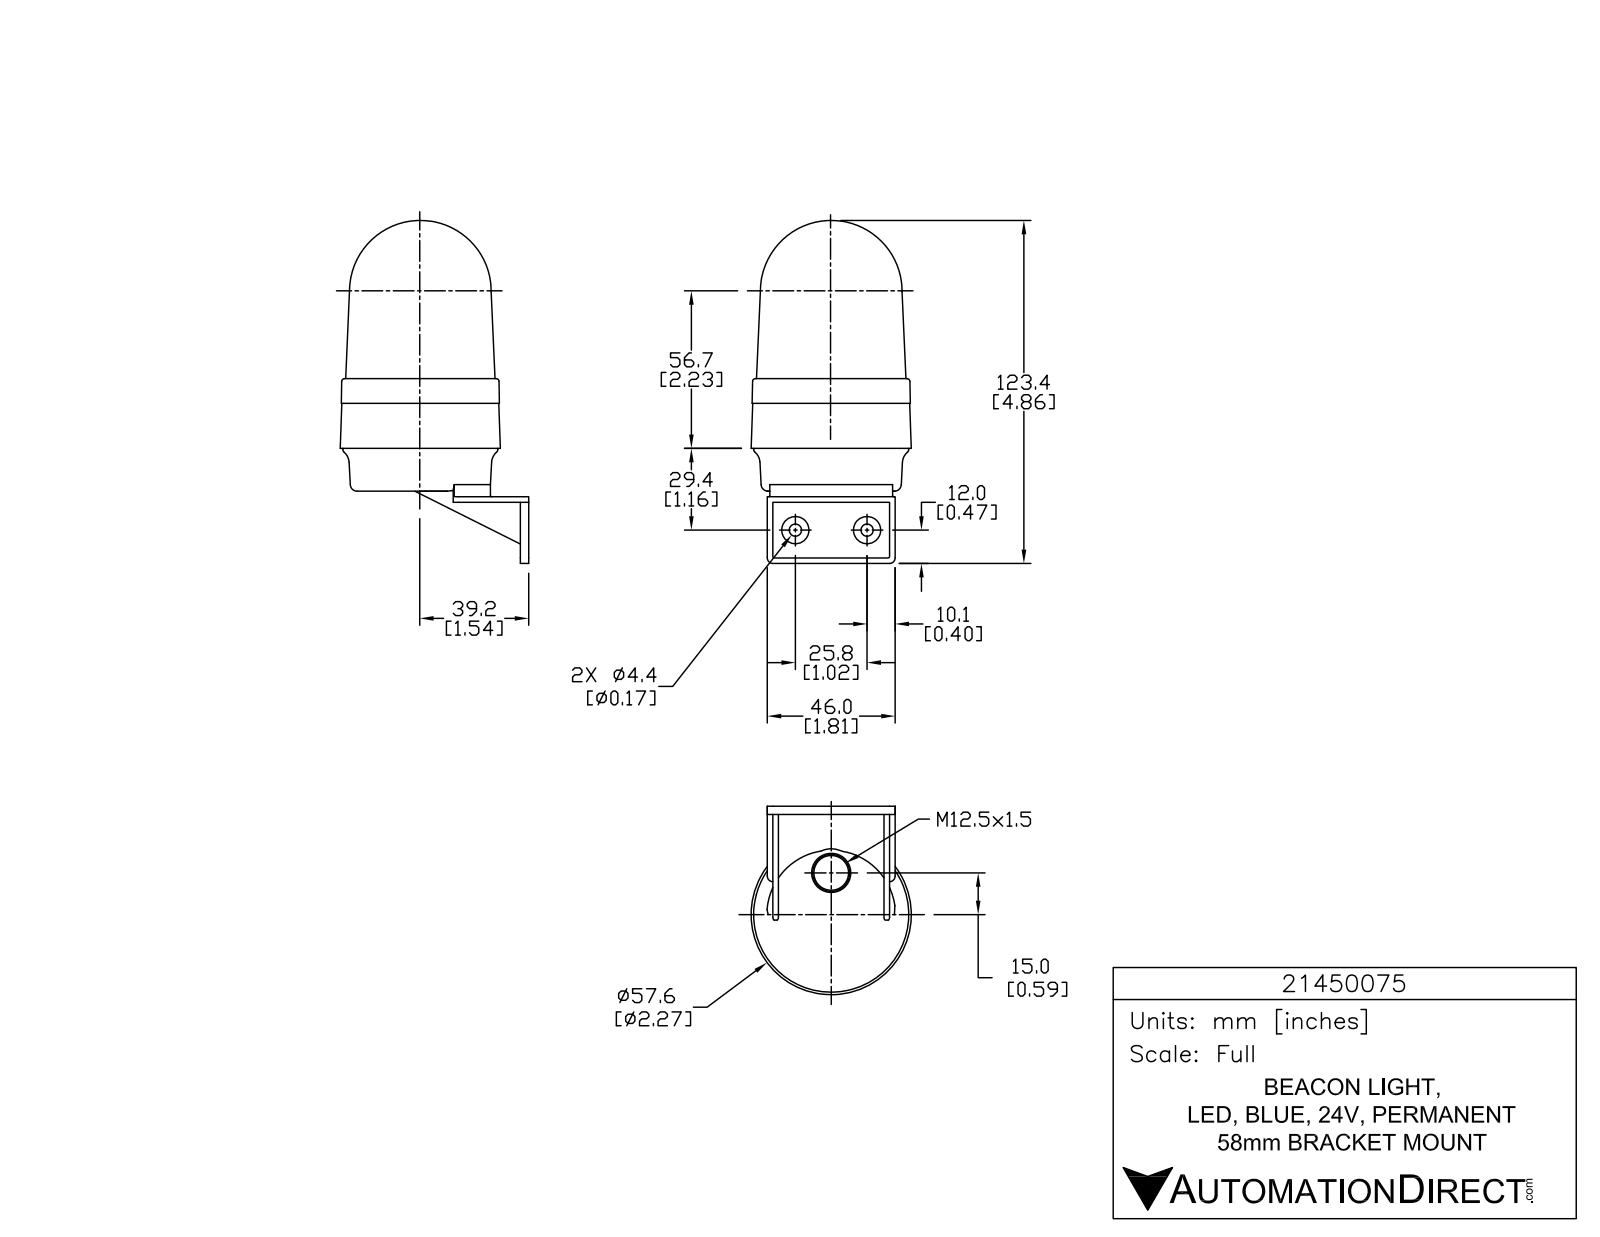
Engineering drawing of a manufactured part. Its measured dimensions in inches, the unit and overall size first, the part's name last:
Units: inches
Overall size (bounding box): 4.858 × 2.852 × 2.407
Round holes (diameter × count): ⌀0.039 ×3, ⌀0.173 ×2
Round bosses / shafts (diameter × count): ⌀0.226 ×3, ⌀0.056 ×3, ⌀0.386 ×2, ⌀2.197 ×1
Partial cylindrical surfaces — rounded edges, fillets, slot ends (radius × count): R0.008 ×6, R0.008 ×6, R0.008 ×6, R0.02 ×6, R0.131 ×6, R0.079 ×4, R0.004 ×3, R0.005 ×3
Main face-to-face distances: 0.079, 0.157, 1.575, 1.654, 0.039, 0.118, 1.496, 0.866, 0.945, 0.764
Hole centre spacings: 1.016
Volume: 12.43 in³ · Surface area: 37.49 in²
Bodies: 1 solid, 828 faces (551 planar, 179 cylindrical, 98 other)
Part name (STEP PRODUCT): 21450075
STEP written by: SolidWorks 2015 (AUTOMOTIVE_DESIGN)
